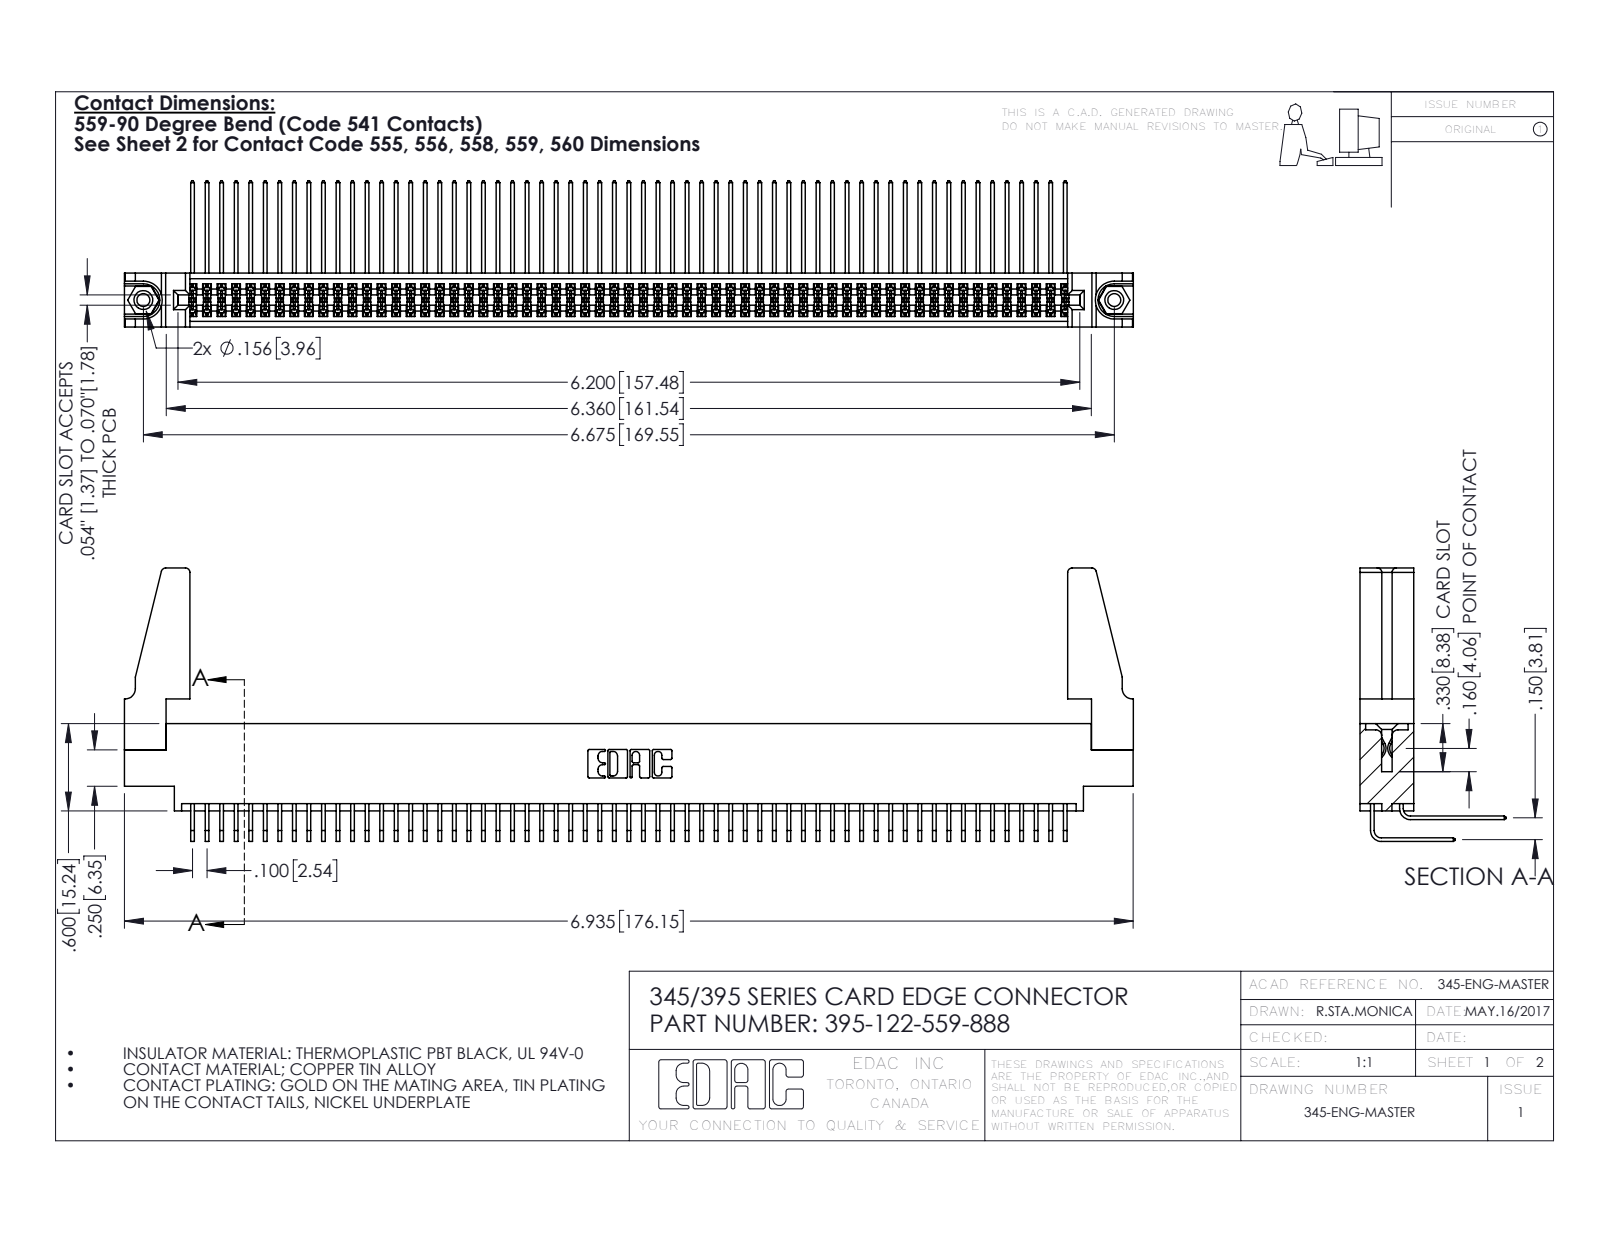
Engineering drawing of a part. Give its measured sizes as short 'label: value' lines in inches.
name: 395-122-559-888; 345-292-001_558 559 Tail - 1; 345-292-001_559 Tail - 2; 345 Part_0.170 Offset - 0.156 Dia-TH (+2 more)
written by: SolidWorks 2016 (CONFIG_CONTROL_DESIGN)
unit: in
bodies: 127 solids, 6598 faces (4426 planar, 2156 cylindrical, 16 other)
size: 6.936 × 1.879 × 1.005
volume: 1.29 in³; area: 51.73 in²
holes: 2× ⌀0.089, 2× ⌀0.125, 2× ⌀0.156, 1× ⌀0.064
bosses: 2× ⌀0.155
rounds: 183× R0.006, 22× R0.01, 8× R0.03, 6× R0.007, 6× R0.031, 3× R0.026, 2× R0.014, 2× R0.019
face distances: 0.072, 0.298, 0.37, 0.098, 0.272, 0.025, 0.2, 0.225, 0.15, 0.175
hole spacings: 0.27, 6.439, 6.675
